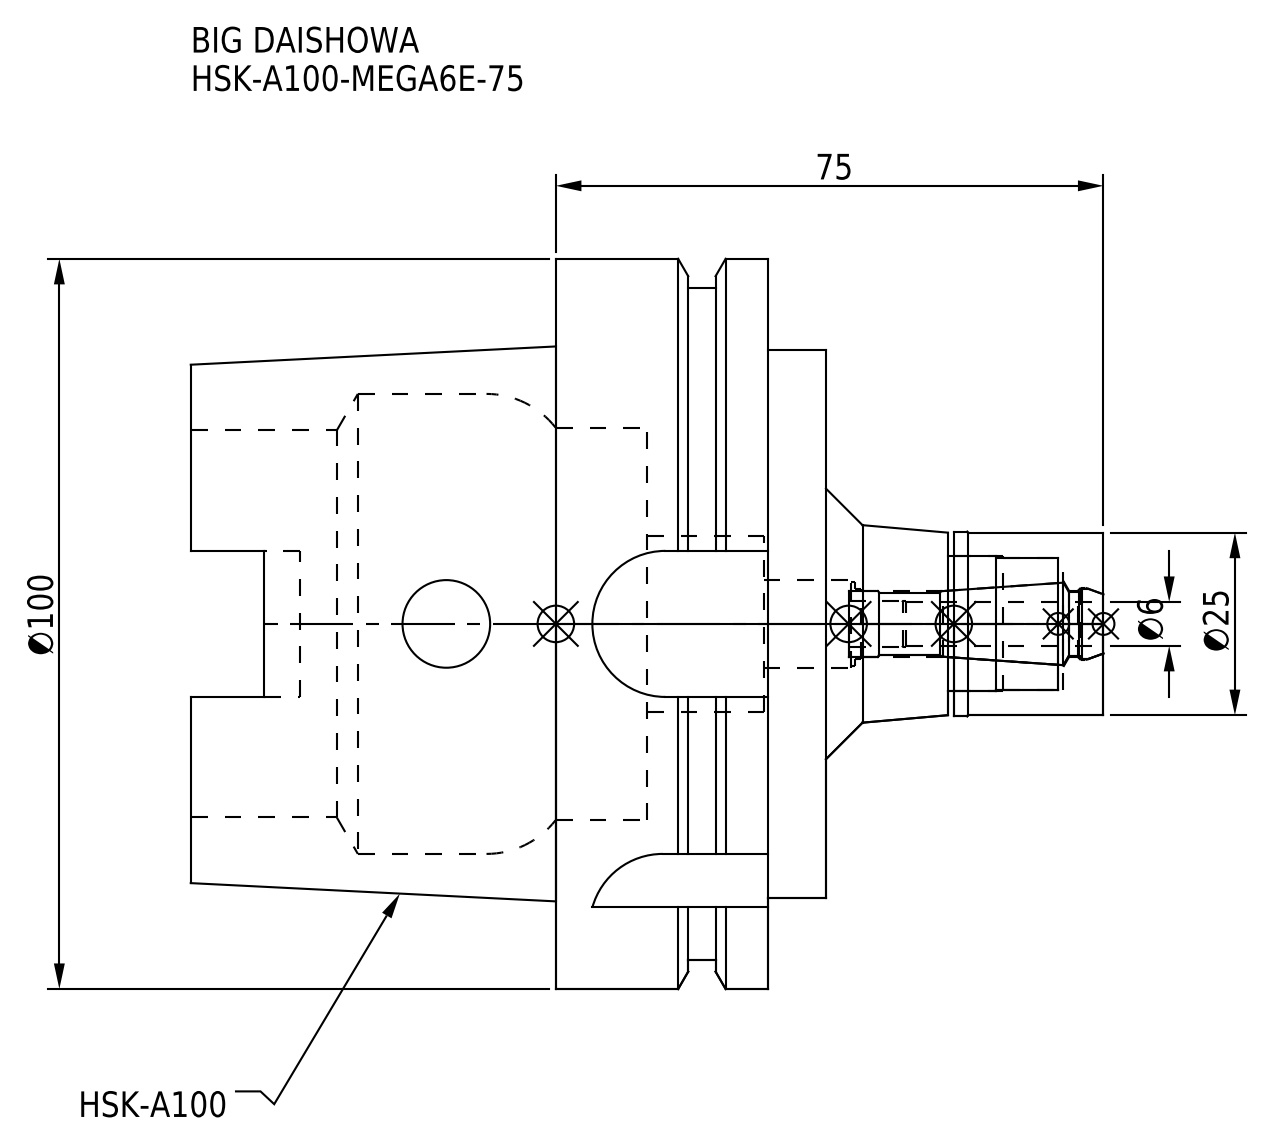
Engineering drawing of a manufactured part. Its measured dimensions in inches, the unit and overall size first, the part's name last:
Units: inches
Overall size (bounding box): 4.921 × 3.937 × 3.937
Round holes (diameter × count): ⌀0.472 ×2, ⌀0.354 ×1, ⌀0.378 ×1, ⌀0.39 ×1, ⌀0.453 ×1, ⌀0.709 ×1, ⌀0.728 ×1, ⌀0.945 ×1, ⌀2.087 ×1, ⌀2.118 ×1, ⌀2.48 ×1
Round bosses / shafts (diameter × count): ⌀3.937 ×1, ⌀3.622 ×1, ⌀2.953 ×1, ⌀0.996 ×1, ⌀0.984 ×1
Partial cylindrical surfaces — rounded edges, fillets, slot ends (radius × count): R0.192 ×4, R0.394 ×4
Main face-to-face distances: 1.457, 0.315, 1.142, 0.49, 0.967, 0.652, 3.425, 3.11, 2.459, 1.969
Volume: 18.65 in³ · Surface area: 90.67 in²
Bodies: 2 solids, 126 faces (42 planar, 56 cylindrical, 28 other)
Part name (STEP PRODUCT): HA100ME06075-060_ASM.stp; HSK-A100-MEGA6E-75_1.stp; HSK-A100-MEGA6E-75; DXF_TEMP_ASSY_ASM_4_ASM.stp (+3 more)
STEP written by: SolidWorks 2019 (CONFIG_CONTROL_DESIGN)
